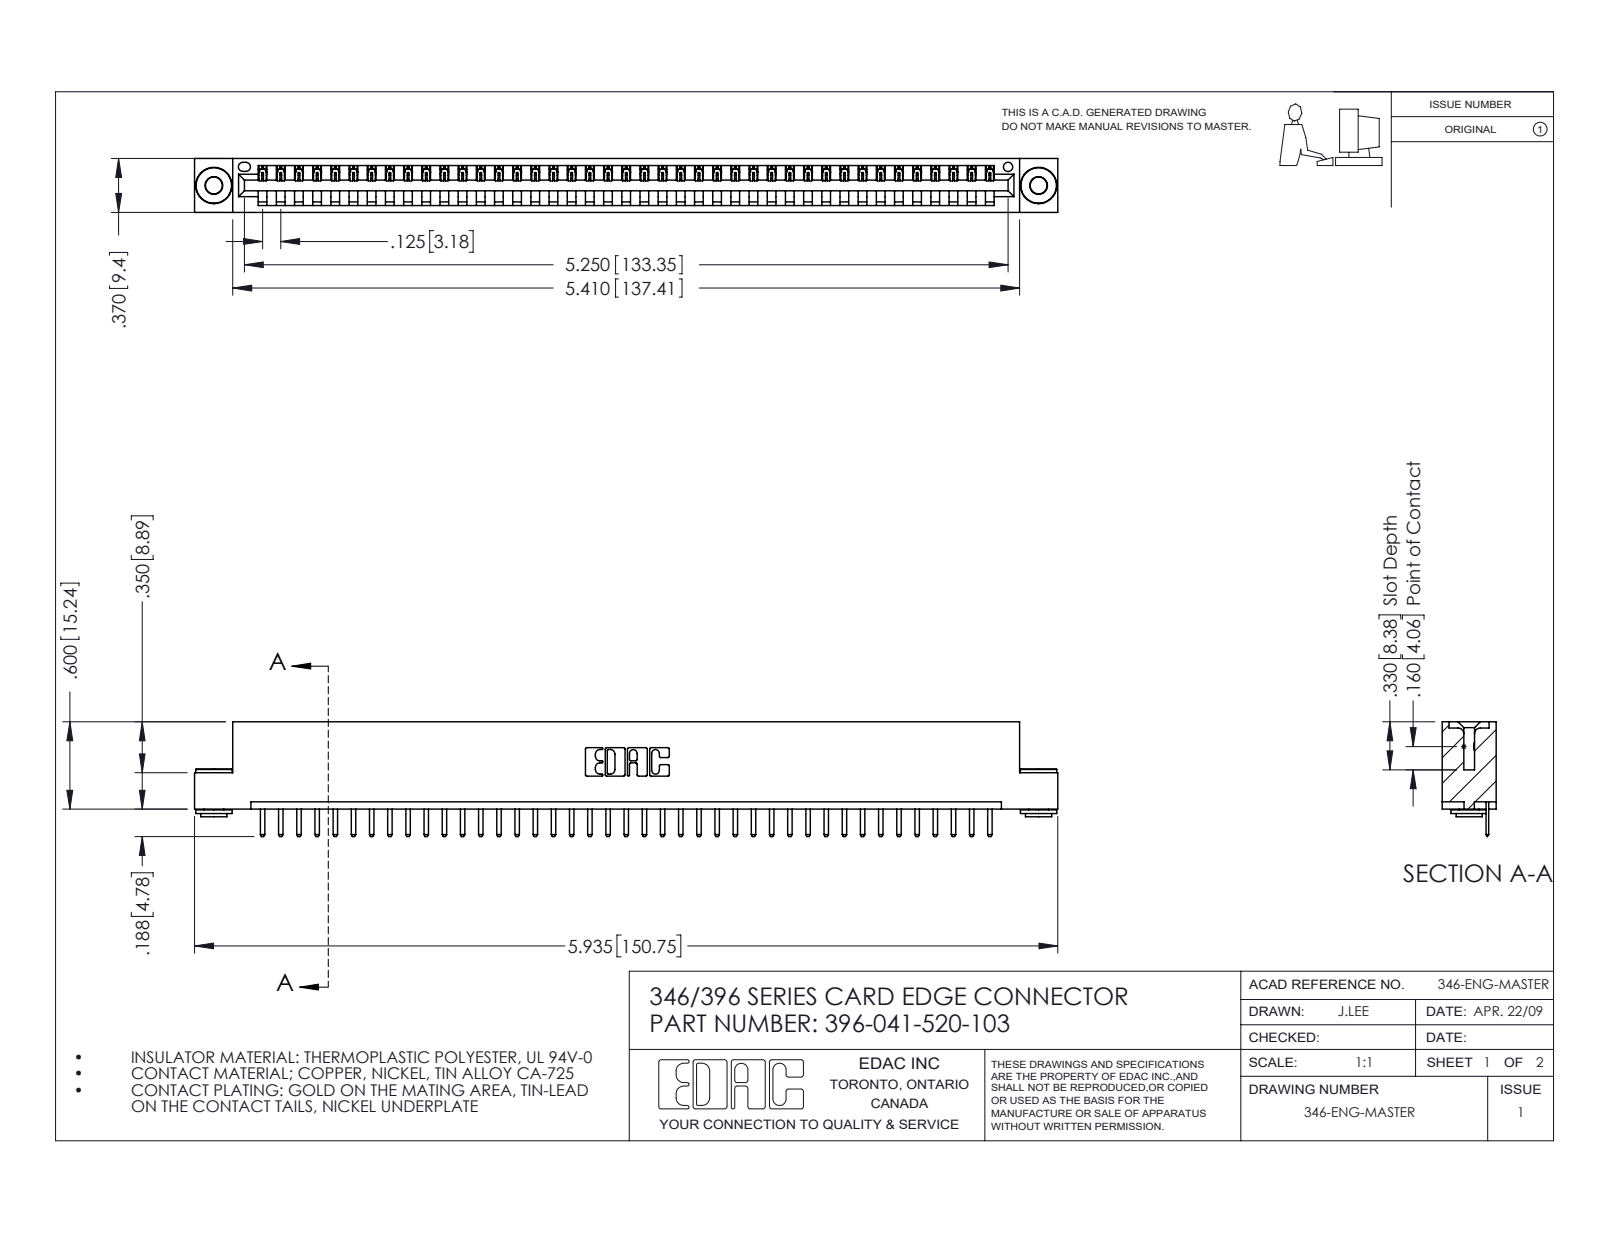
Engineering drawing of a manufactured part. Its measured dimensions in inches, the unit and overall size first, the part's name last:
Units: inches
Overall size (bounding box): 5.935 × 0.788 × 0.37
Round holes (diameter × count): ⌀0.116 ×2, ⌀0.156 ×2, ⌀0.064 ×1
Round bosses / shafts (diameter × count): ⌀0.25 ×2, ⌀0.18 ×2, ⌀0.136 ×2
Partial cylindrical surfaces — rounded edges, fillets, slot ends (radius × count): R0.01 ×84, R0.006 ×82, R0.01 ×22, R0.007 ×6, R0.031 ×6, R0.026 ×3, R0.031 ×2, R0.04 ×2
Main face-to-face distances: 0.048, 0.322, 0.37, 0.25, 0.148, 0.222, 0.1, 0.174, 0.025, 0.072
Hole centre spacings: 0.246, 5.461, 5.67
Volume: 0.874 in³ · Surface area: 27.46 in²
Bodies: 44 solids, 2702 faces (1808 planar, 886 cylindrical, 8 other)
Part name (STEP PRODUCT): 345-250-002_345-250-002-102; 396-041-520-103; 345-292-001_345-293-120; 346 Part_Flush Mounting Lugs - 0.156 Dia-TH
STEP written by: SolidWorks 2016 (CONFIG_CONTROL_DESIGN)
